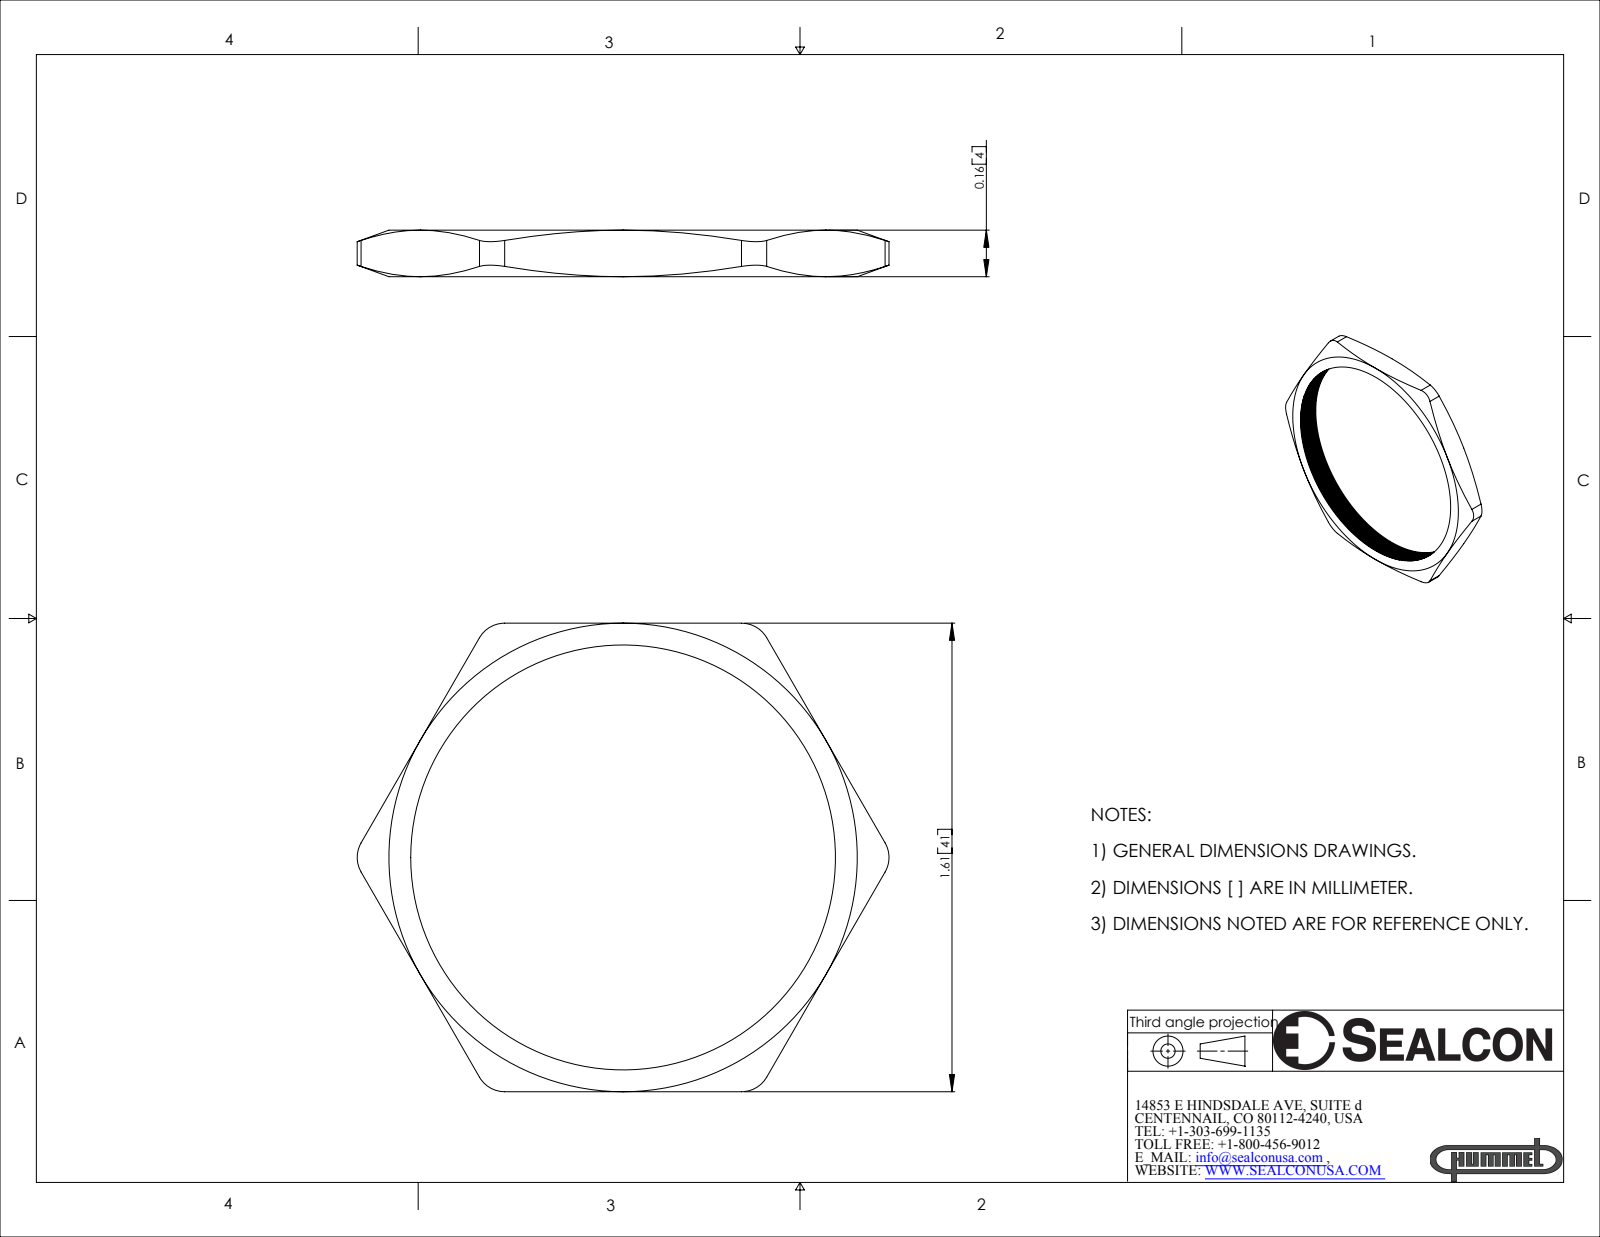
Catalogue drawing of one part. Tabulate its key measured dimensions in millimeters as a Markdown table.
| quantity | value |
| --- | --- |
| part name | NP-29-BR |
| STEP written by | SolidWorks 2007 (CONFIG_CONTROL_DESIGN) |
| units | millimeters |
| bodies | 1 solid, 107 faces (8 planar, 7 cylindrical, 92 other) |
| overall size | 46.4 × 40.9 × 4.1 |
| volume | 1 300 mm³ |
| surface area | 2 132 mm² |
| partial cylindrical surfaces (radius × count) | 2.5 × 6 |
| main face-to-face distances | 40.9, 4.1 |
